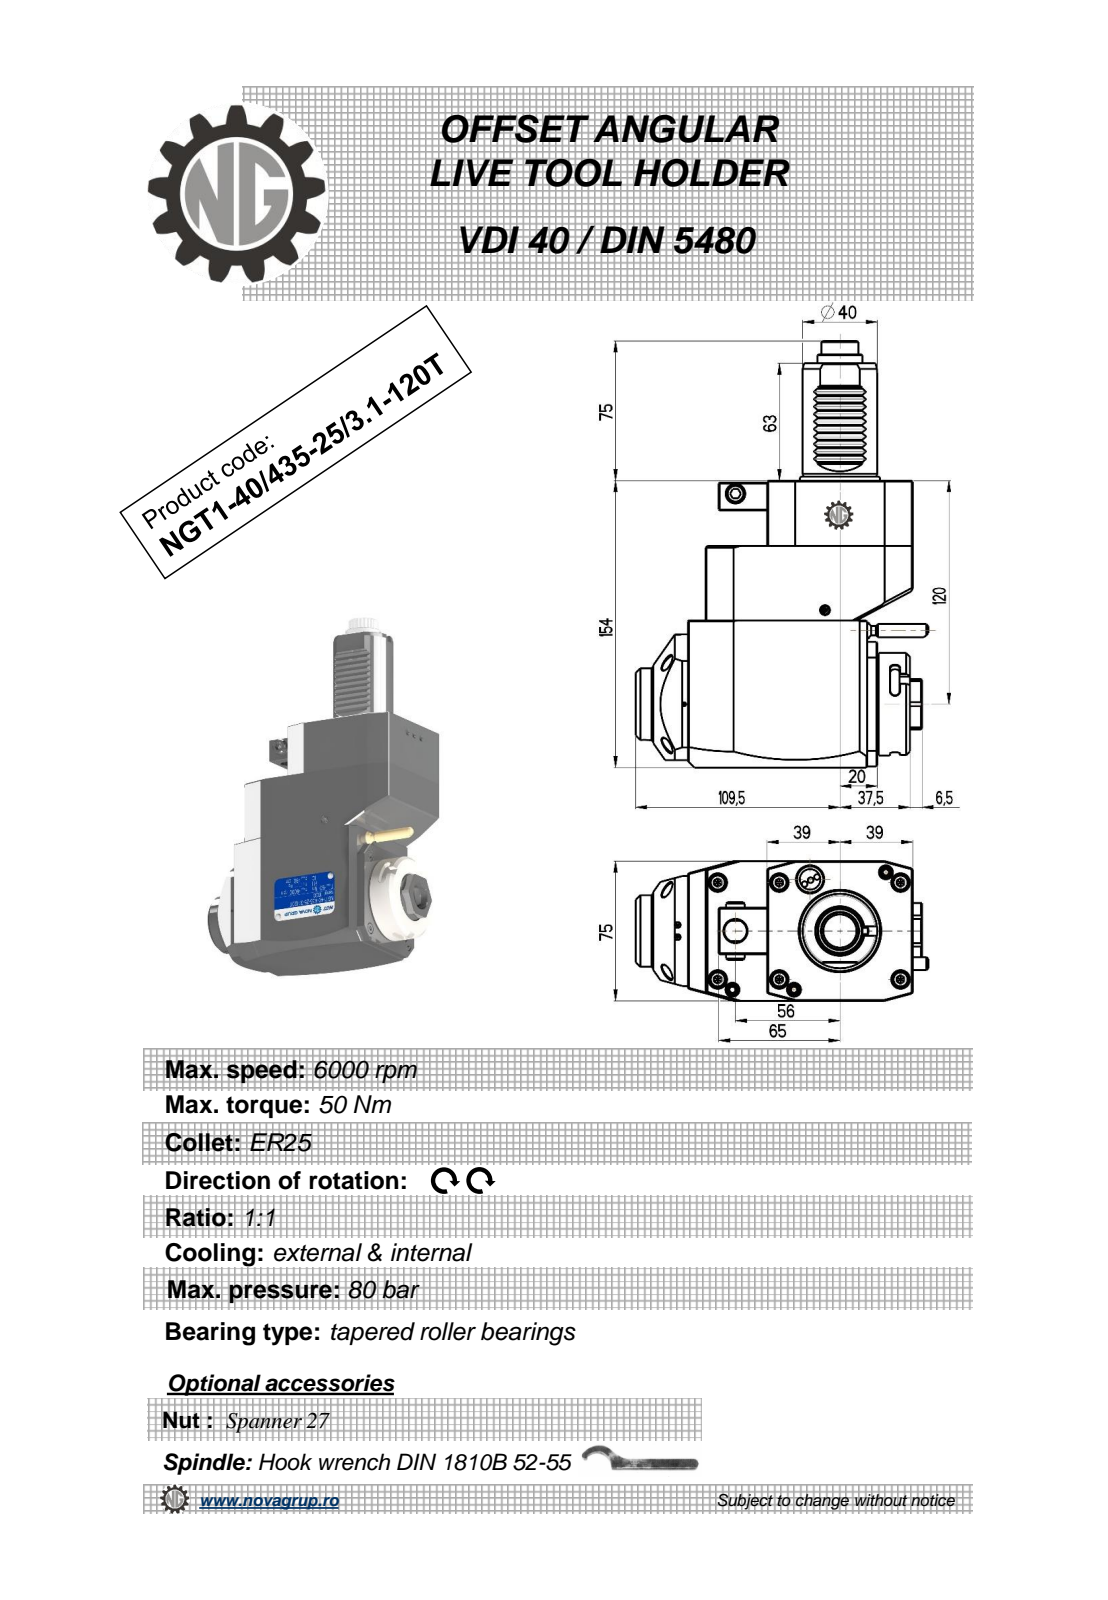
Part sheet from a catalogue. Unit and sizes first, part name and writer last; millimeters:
Units: millimetres
Overall size (bounding box): 229 × 156.83 × 75
Round holes (diameter × count): ⌀2.5 ×1, ⌀3 ×1, ⌀8.5 ×1, ⌀9.5 ×1, ⌀12 ×1, ⌀18 ×1
Round bosses / shafts (diameter × count): ⌀8.96 ×2, ⌀55 ×1, ⌀48 ×1, ⌀40 ×1, ⌀38.5 ×1, ⌀24 ×1, ⌀10 ×1, ⌀7 ×1
Partial cylindrical surfaces — rounded edges, fillets, slot ends (radius × count): R2.08 ×48, R0.3 ×10, R2.5 ×6, R15 ×2, R180 ×2, R9.08 ×1, R9.92 ×1, R24.5 ×1
Main face-to-face distances: 75, 154, 119, 19, 111, 92, 35, 59, 33, 78
Hole centre spacings: 43.2, 74.1, 111.5
Volume: 1 281 000 mm³ · Surface area: 89 463 mm²
Bodies: 1 solid, 453 faces (189 planar, 168 cylindrical, 96 other)
Part name (STEP PRODUCT): NGT1_40_435_25_3_1_120T
STEP written by: PRO/ENGINEER BY PARAMETRIC TECHNOLOGY CORPORATION, 2010280 (CONFIG_CONTROL_DESIGN)
